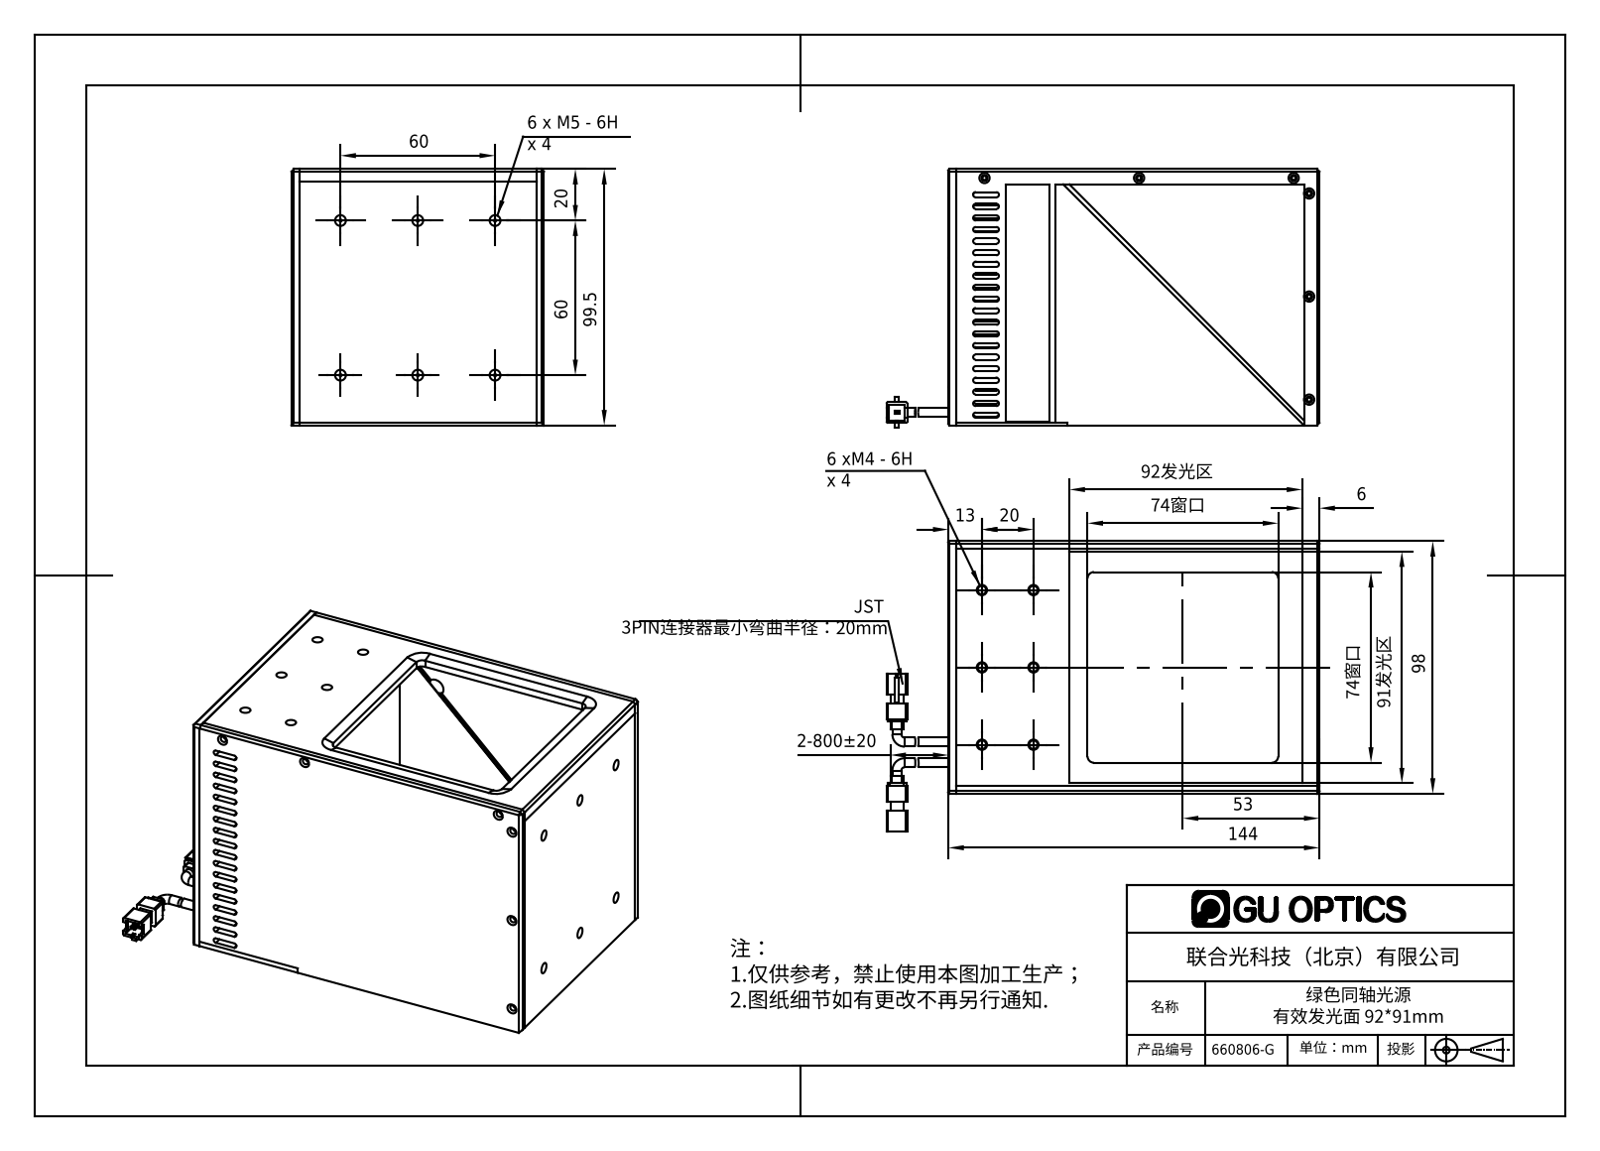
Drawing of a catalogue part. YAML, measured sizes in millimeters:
part_name: "绿色同轴光源 有效发光面 9291mm"
step_written_by: "SolidWorks 2016 (AUTOMOTIVE_DESIGN)"
units: millimeters
bodies: {solids: 22, faces: 4262, planar: 906, cylindrical: 2251, other: 1105}
overall_size: [168, 110.5, 99.7]
volume: 274829
surface_area: 199655
round_holes:
  - {diameter: 1.6, count: 16}
  - {diameter: 2.4, count: 16}
  - {diameter: 2, count: 14}
  - {diameter: 3.3, count: 6}
  - {diameter: 4, count: 6}
  - {diameter: 4.2, count: 6}
  - {diameter: 2.5, count: 4}
  - {diameter: 7, count: 4}
  - {diameter: 1, count: 2}
  - {diameter: 6.8, count: 2}
  - {diameter: 38, count: 1}
  - {diameter: 48, count: 1}
round_bosses_or_shafts:
  - {diameter: 3.8, count: 462}
  - {diameter: 3, count: 462}
  - {diameter: 3.5, count: 3}
  - {diameter: 51, count: 1}
  - {diameter: 41, count: 1}
partial_cylinders:
  - {radius: 1, count: 76}
  - {radius: 0.5, count: 8}
  - {radius: 1.76, count: 8}
  - {radius: 1.76, count: 8}
  - {radius: 1.77, count: 8}
  - {radius: 2, count: 8}
  - {radius: 2.5, count: 4}
  - {radius: 1.01, count: 2}
face_to_face_distances: [4, 94, 2, 3, 98, 6, 90, 1, 141, 135]
hole_center_spacings: [30, 60, 50, 23.41, 35.36, 36.06, 67.08, 72.1]
